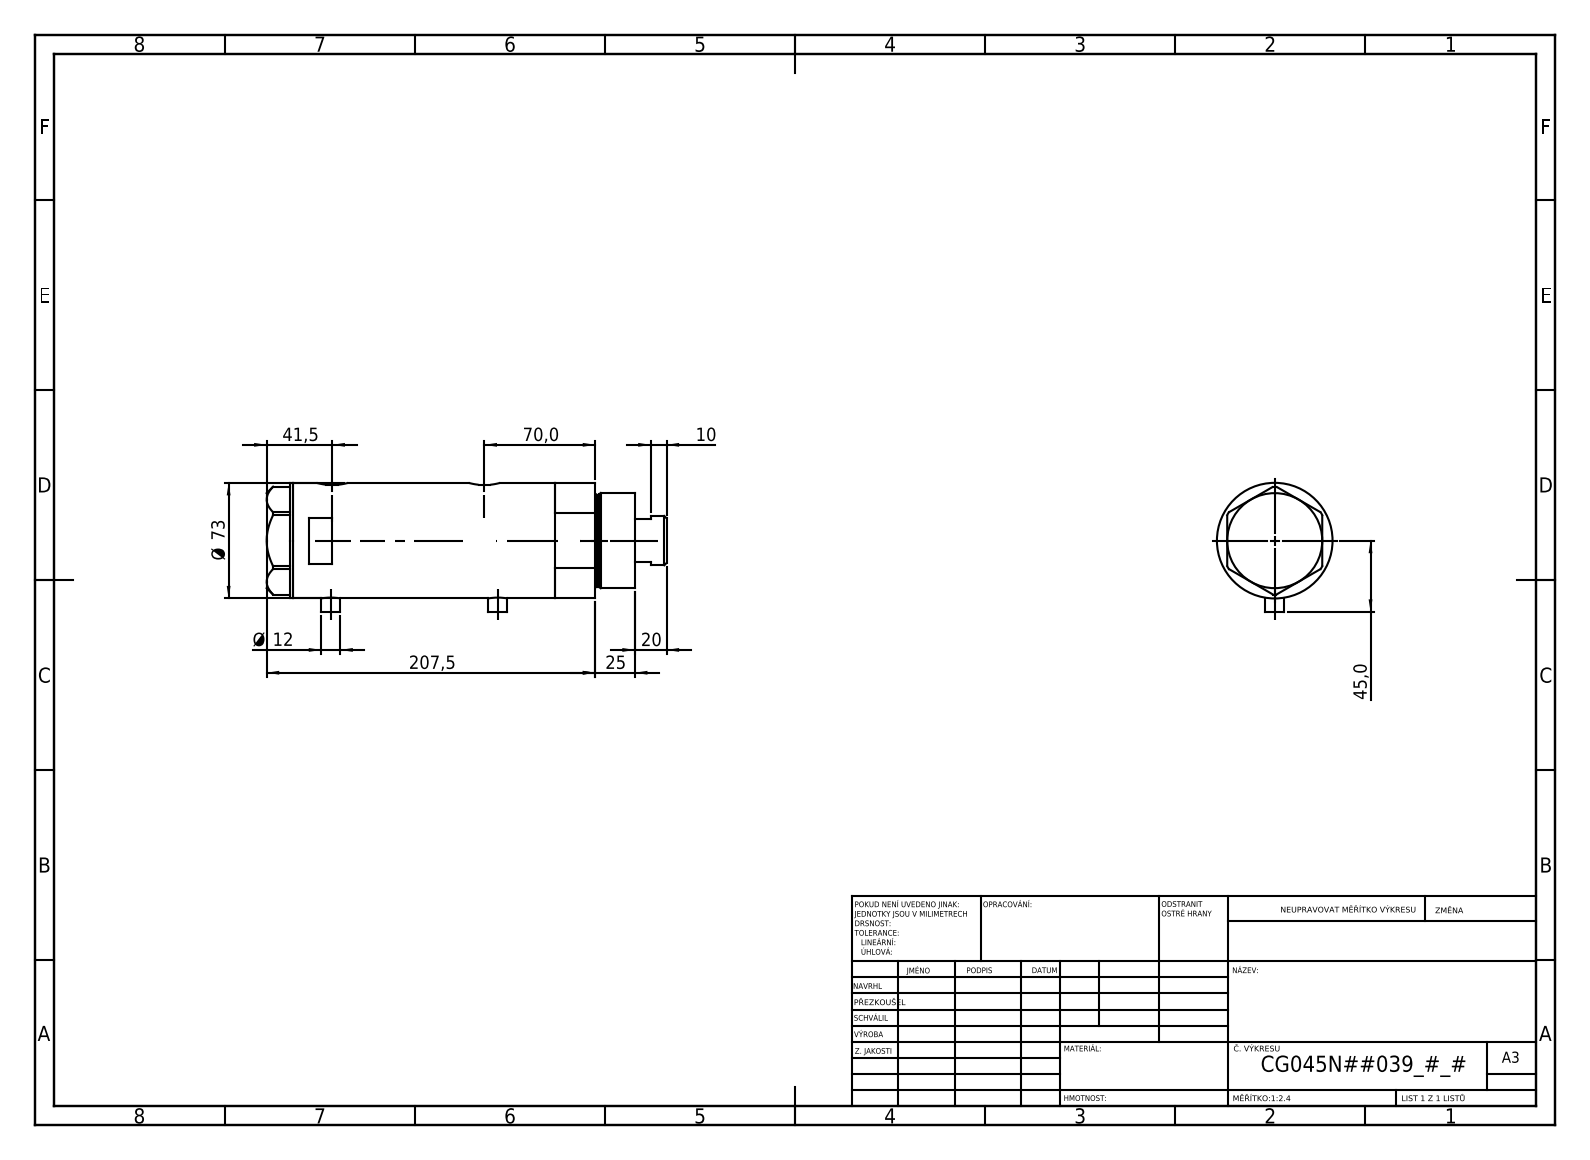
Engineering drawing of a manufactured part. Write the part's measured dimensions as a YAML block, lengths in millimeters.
part_name: "V270CG_MIDDLE; V270CG_BACK; V270CG_VC; V270CG_FRONT"
step_written_by: "SolidWorks 2019 (CONFIG_CONTROL_DESIGN)"
units: millimeters
bodies: {solids: 4, faces: 120, planar: 49, cylindrical: 51, other: 20}
overall_size: [252.5, 81.5, 73]
volume: 894792
surface_area: 149400
round_holes:
  - {diameter: 12.5, count: 2}
  - {diameter: 13.16, count: 2}
  - {diameter: 10.5, count: 1}
  - {diameter: 32, count: 1}
  - {diameter: 33.5, count: 1}
  - {diameter: 45, count: 1}
  - {diameter: 48, count: 1}
  - {diameter: 64, count: 1}
round_bosses_or_shafts:
  - {diameter: 12, count: 2}
  - {diameter: 73, count: 1}
  - {diameter: 60, count: 1}
  - {diameter: 58, count: 1}
  - {diameter: 31, count: 1}
partial_cylinders:
  - {radius: 10, count: 2}
face_to_face_distances: [95, 121, 26, 16.5, 42.5, 137.5, 2, 216, 232.5, 190]
hole_center_spacings: [1, 8.5, 96, 97, 104.5, 105.5]
